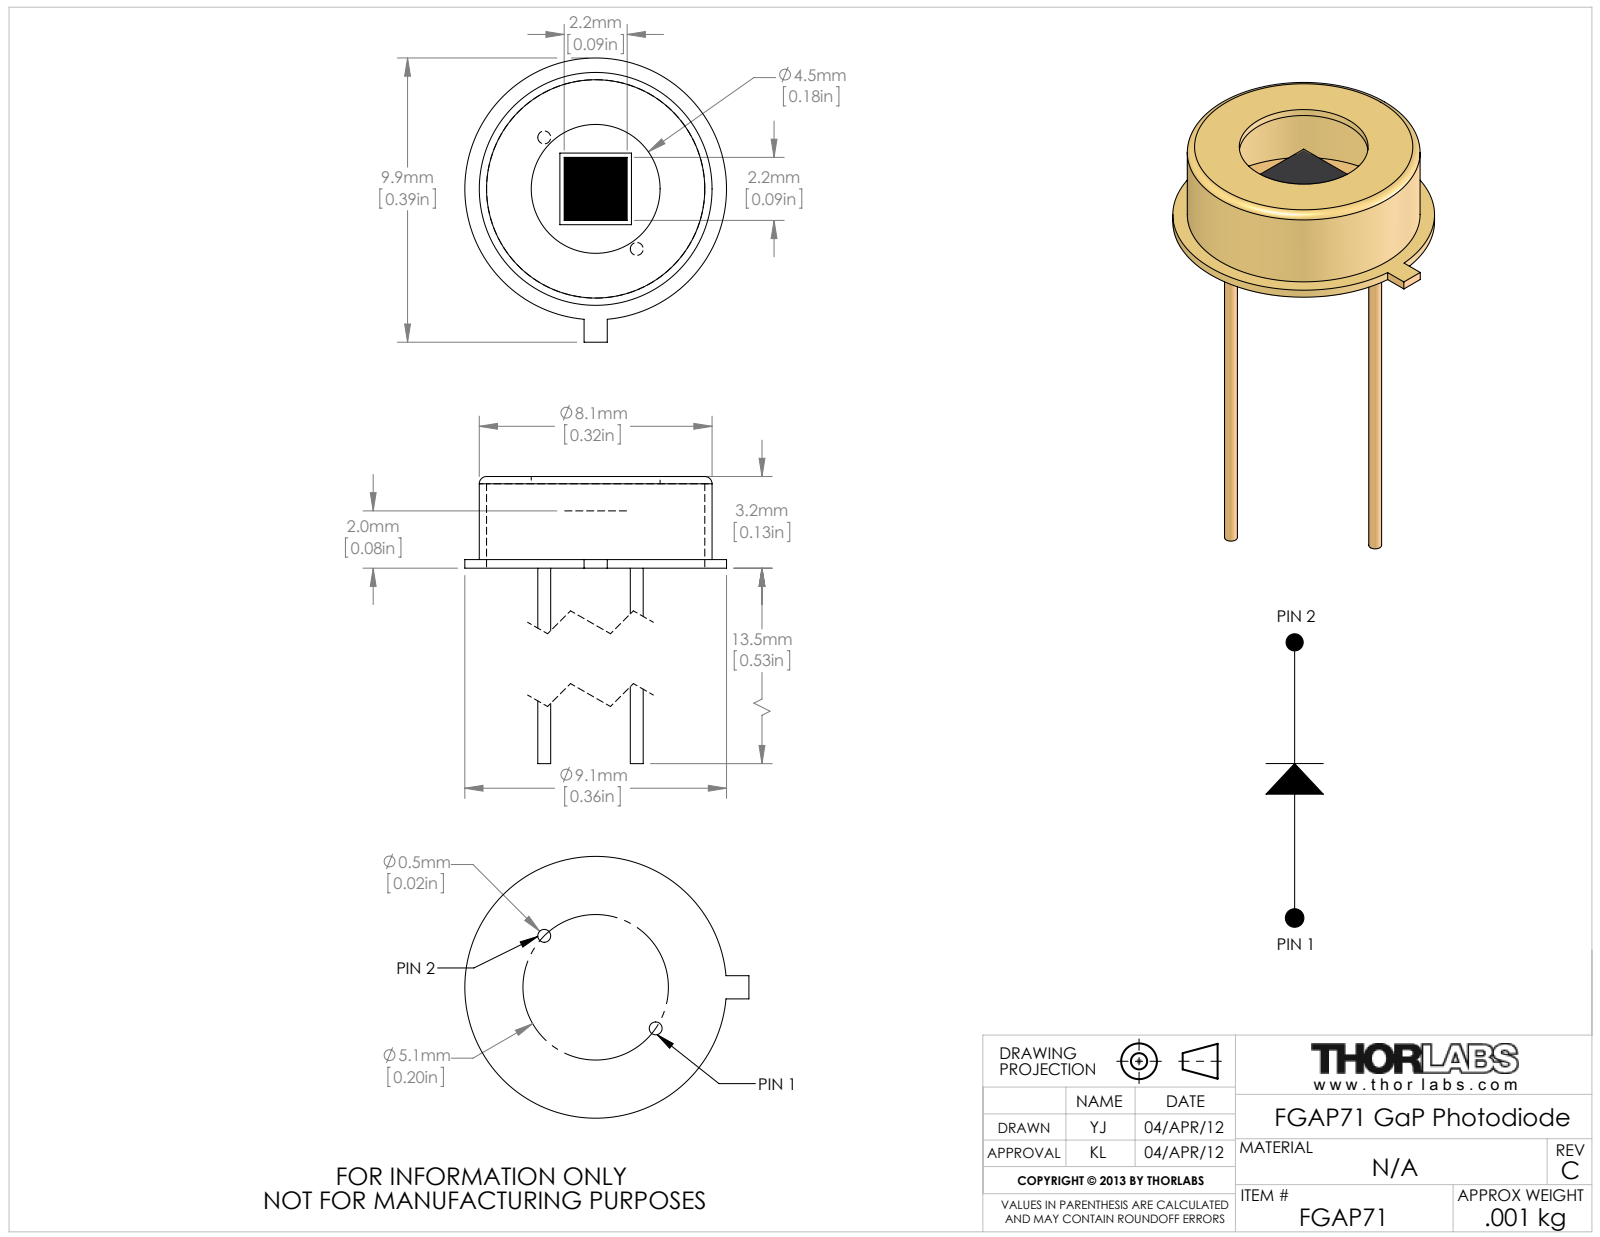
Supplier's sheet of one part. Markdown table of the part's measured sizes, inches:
| quantity | value |
| --- | --- |
| part name | 12174-E0W |
| STEP written by | SolidWorks 2012 (AUTOMOTIVE_DESIGN) |
| units | inches |
| bodies | 2 solids, 36 faces (21 planar, 13 cylindrical, 2 other) |
| overall size | 0.657 × 0.391 × 0.36 |
| volume | 0.002 in³ |
| surface area | 0.617 in² |
| round holes (diameter × count) | 0.177 × 1, 0.3 × 1 |
| round bosses / shafts (diameter × count) | 0.018 × 2, 0.36 × 1, 0.32 × 1 |
| main face-to-face distances | 0.114, 0.116, 0.126, 0.124, 0.104, 0.057, 0.067, 0.047, 0.069, 0.079 |
